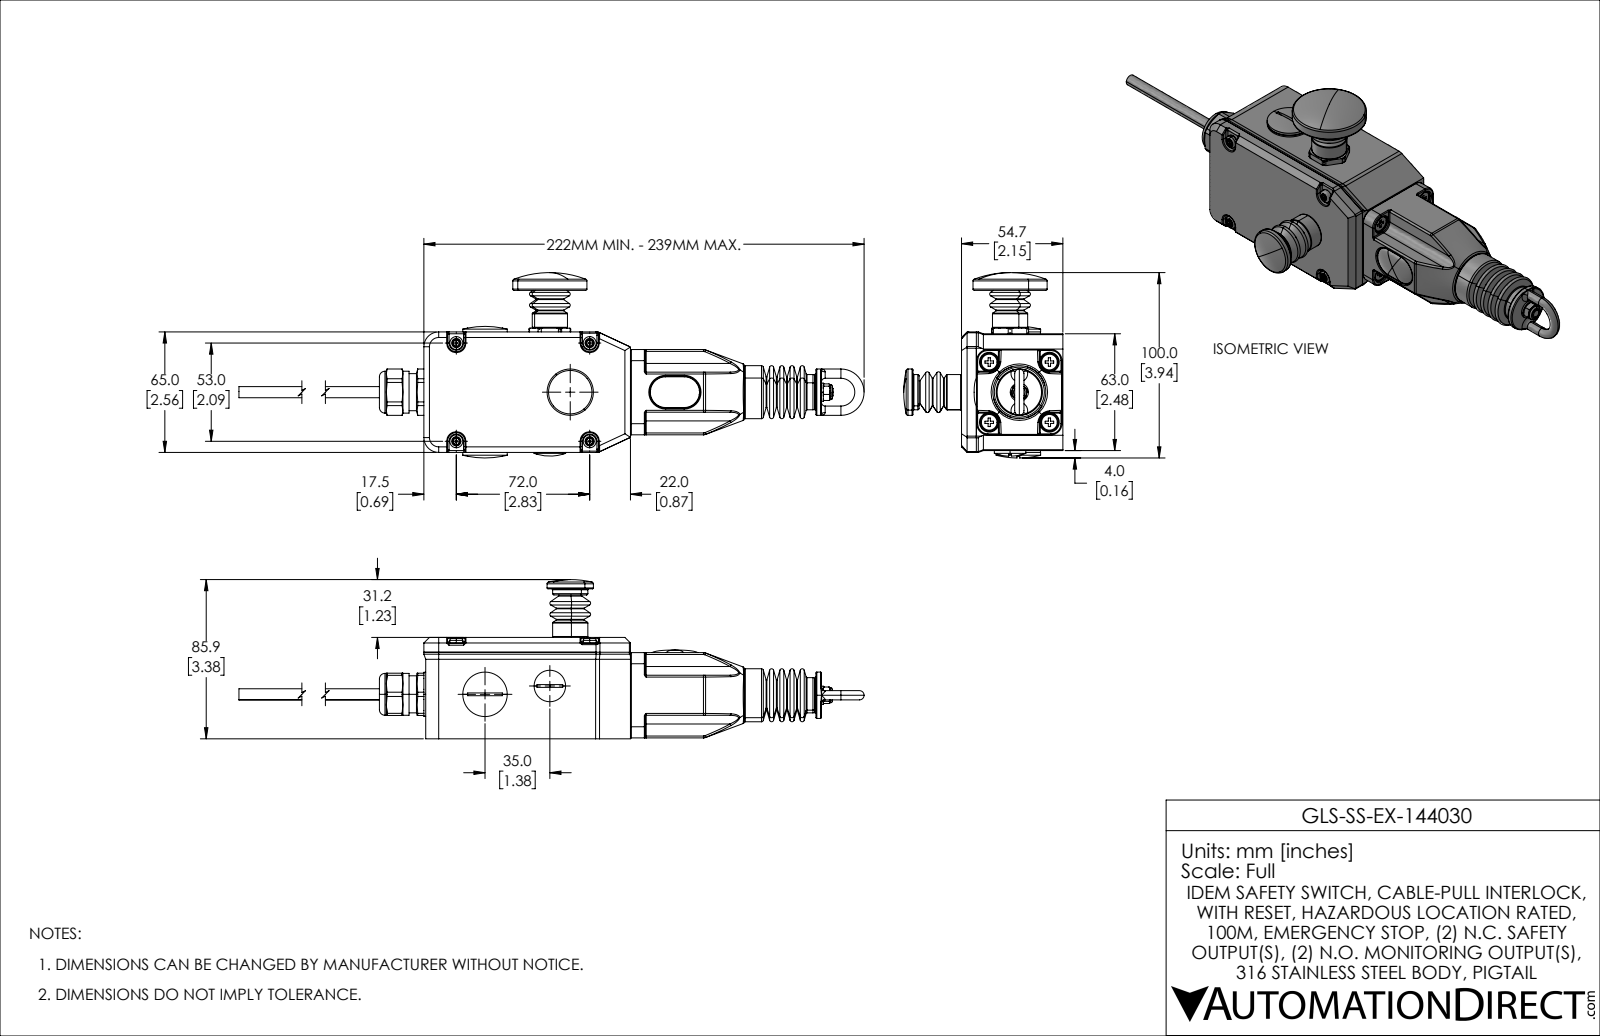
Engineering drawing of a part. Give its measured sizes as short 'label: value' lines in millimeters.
name: GLS-SS-EX-144030
written by: SolidWorks 2021 (AUTOMOTIVE_DESIGN)
unit: mm
bodies: 33 solids, 3146 faces (824 planar, 1098 cylindrical, 1224 other)
size: 326.1 × 100 × 85.9
volume: 234 700 mm³; area: 147 500 mm²
holes: 8× ⌀5.4, 6× ⌀2.7, 5× ⌀3.5, 4× ⌀4, 4× ⌀4.1, 4× ⌀4.6, 4× ⌀5, 4× ⌀9.6, 4× ⌀9.7, 3× ⌀2.1, 3× ⌀15, 2× ⌀2.4
bosses: 7× ⌀5, 5× ⌀7, 5× ⌀6.5, 4× ⌀8.5, 4× ⌀4.4, 4× ⌀1.3, 3× ⌀19, 2× ⌀25
rounds: 225× R0.5, 130× R1, 48× R0.2, 18× R0.3, 14× R0.2, 13× R0.8, 12× R0.7, 12× R5
face distances: 3.5, 51, 54, 5, 3, 8, 7, 46, 63, 3.3
hole spacings: 32.5, 23, 23, 32.5, 32.5, 36.3, 46, 60.4
